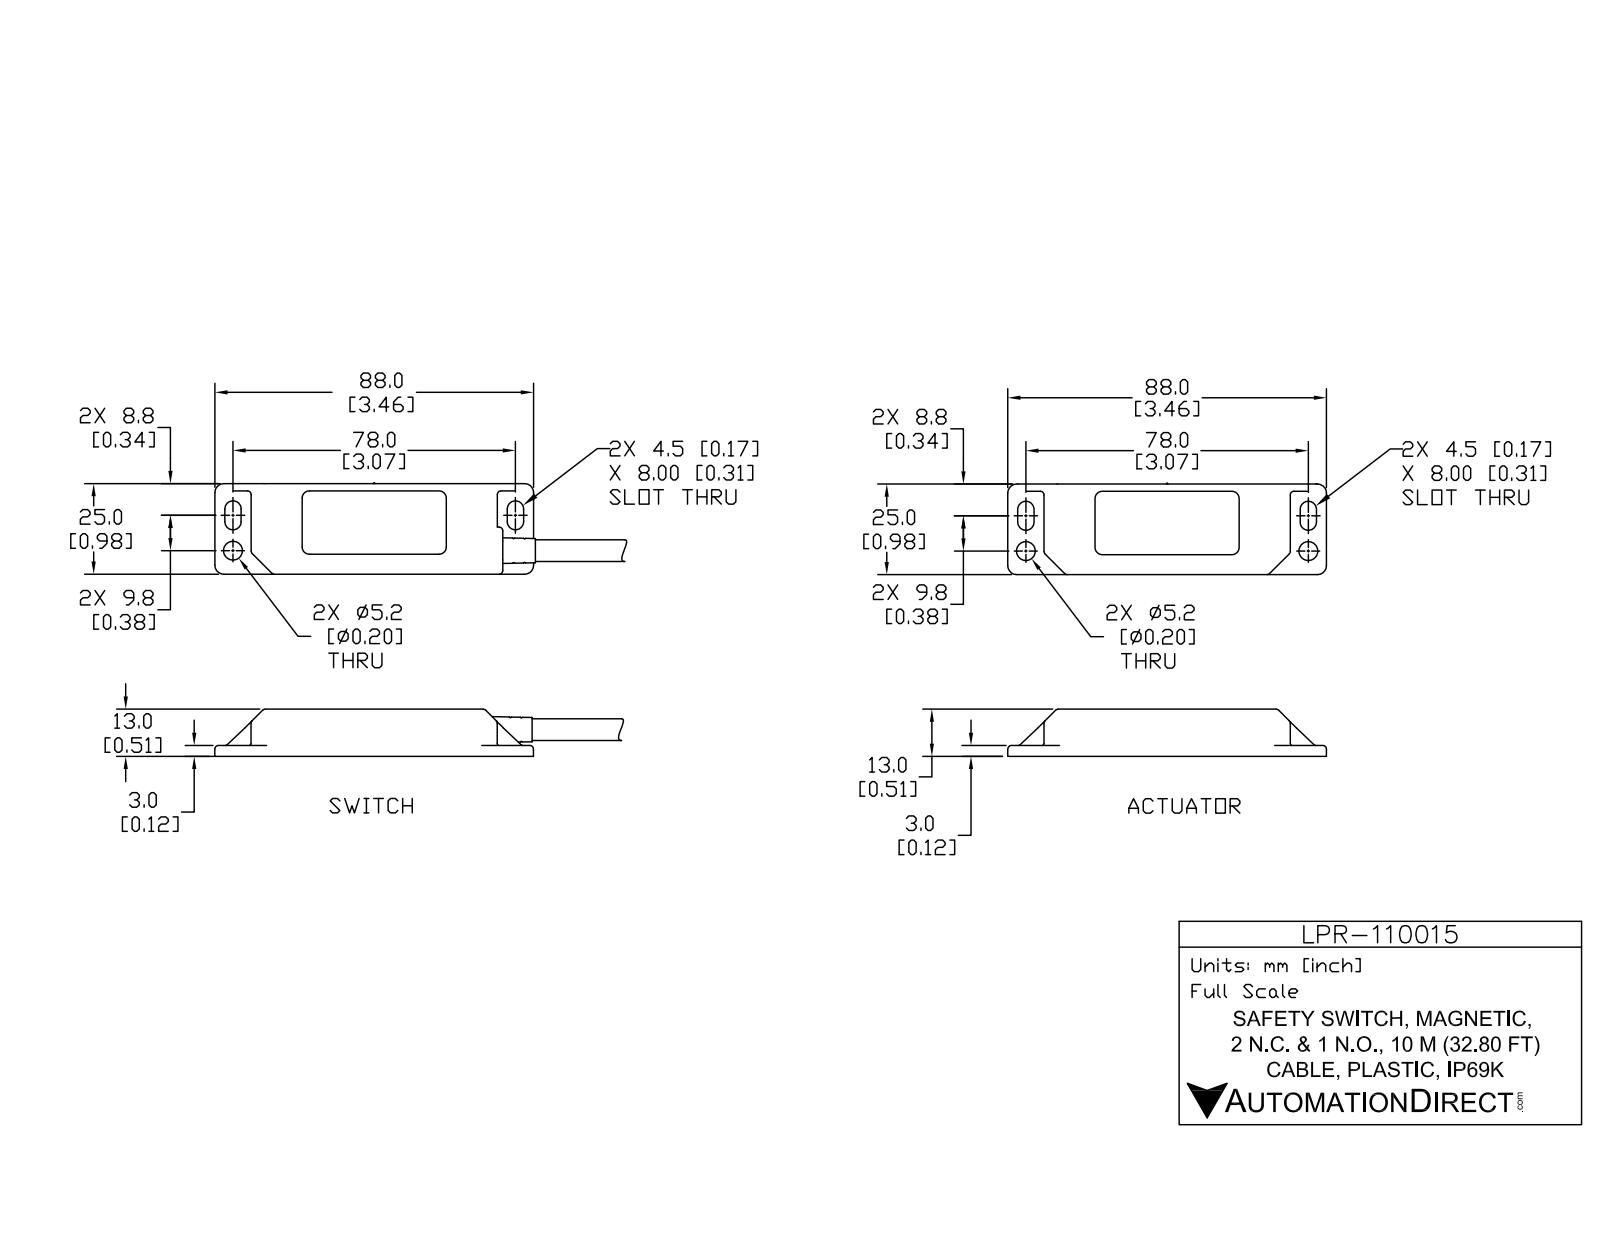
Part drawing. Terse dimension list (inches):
name: LPR-110015_2; LPR-110015; LPR-110015_1
written by: SolidWorks 2017 (AUTOMOTIVE_DESIGN)
unit: in
bodies: 11 solids, 1058 faces (401 planar, 303 cylindrical, 354 other)
size: 8.849 × 1.992 × 0.543
volume: 1.638 in³; area: 46.88 in²
holes: 4× ⌀0.197, 4× ⌀0.205, 1× ⌀0.119, 1× ⌀0.173, 1× ⌀0.213, 1× ⌀0.232, 1× ⌀0.276
bosses: 4× ⌀0.079, 2× ⌀0.193, 2× ⌀0.091, 1× ⌀0.339, 1× ⌀0.299, 1× ⌀0.28, 1× ⌀0.236, 1× ⌀0.209
rounds: 116× R0.02, 49× R0.039, 10× R0.079, 8× R0.089, 8× R0.098, 6× R0.012, 1× R0.189
face distances: 0.067, 0.441, 0.079, 0.374, 0.059, 0.071, 0.508, 0.445, 0.512, 0.988
hole spacings: 0.748, 1.097, 1.19, 1.275, 1.48, 1.571, 1.784, 1.895
